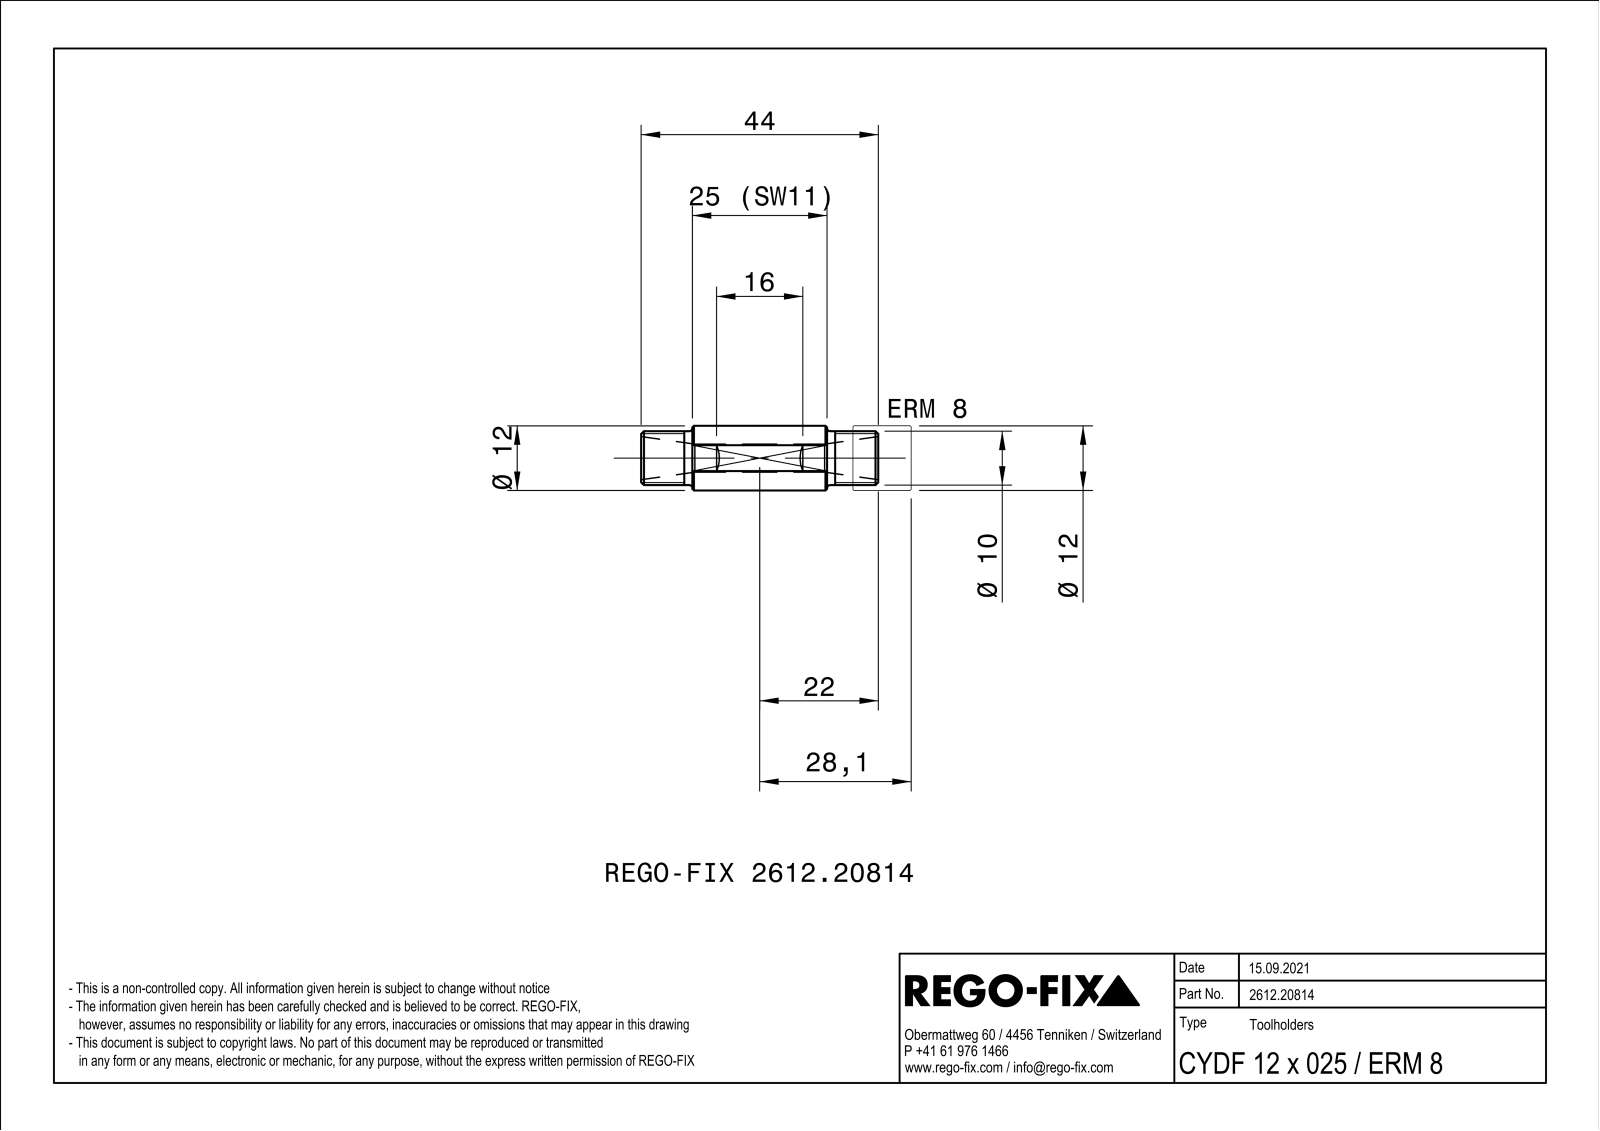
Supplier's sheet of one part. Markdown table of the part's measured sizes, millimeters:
| quantity | value |
| --- | --- |
| part name | NOCUT |
| STEP written by | SIEMENS PLM Software Solid Edge ST10 (AUTOMOTIVE_DESIGN) |
| units | millimeters |
| bodies | 1 solid, 29 faces (11 planar, 6 cylindrical, 12 other) |
| overall size | 44 × 12 × 11.5 |
| volume | 3 055 mm³ |
| surface area | 2 416 mm² |
| round holes (diameter × count) | 5.2 × 1 |
| round bosses / shafts (diameter × count) | 12 × 1, 10 × 1 |
| main face-to-face distances | 11, 44, 9.5, 34.5, 25 |
